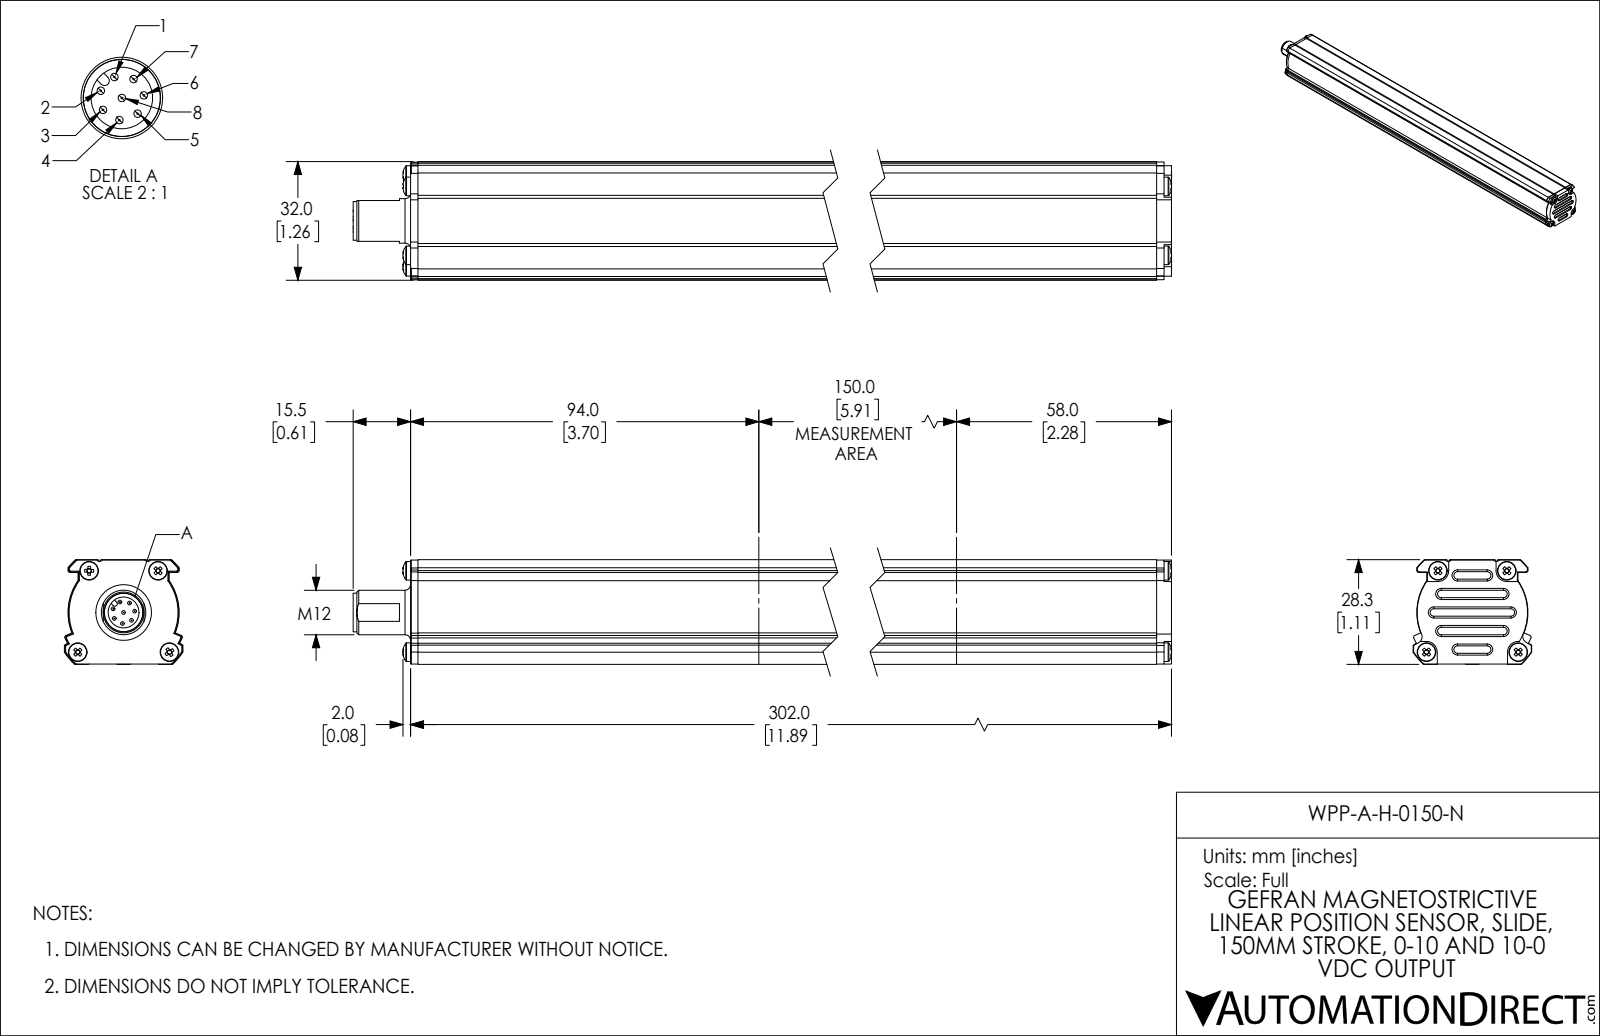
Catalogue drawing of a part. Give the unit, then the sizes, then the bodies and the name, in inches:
Units: inches
Overall size (bounding box): 12.502 × 1.26 × 1.112
Round holes (diameter × count): ⌀0.091 ×4, ⌀0.102 ×4, ⌀0.276 ×1, ⌀0.327 ×1, ⌀0.37 ×1
Round bosses / shafts (diameter × count): ⌀0.039 ×8, ⌀0.197 ×4, ⌀0.472 ×1, ⌀0.409 ×1, ⌀0.376 ×1, ⌀0.315 ×1
Partial cylindrical surfaces — rounded edges, fillets, slot ends (radius × count): R0.02 ×8, R0.114 ×4, R0.016 ×2, R0.039 ×2, R0.073 ×2, R0.026 ×1, R0.079 ×1, R0.587 ×1
Main face-to-face distances: 1.102, 1.112, 11.654, 0.976, 0.967, 0.136, 0.146, 1.114, 0.079, 11.732
Hole centre spacings: 0.575, 0.644, 0.732, 0.872, 0.873, 0.974, 1.214, 1.215
Volume: 14.73 in³ · Surface area: 83.09 in²
Bodies: 20 solids, 573 faces (301 planar, 131 cylindrical, 141 other)
Part name (STEP PRODUCT): WPP-A-H-0150-N
STEP written by: SolidWorks 2021 (CONFIG_CONTROL_DESIGN)
